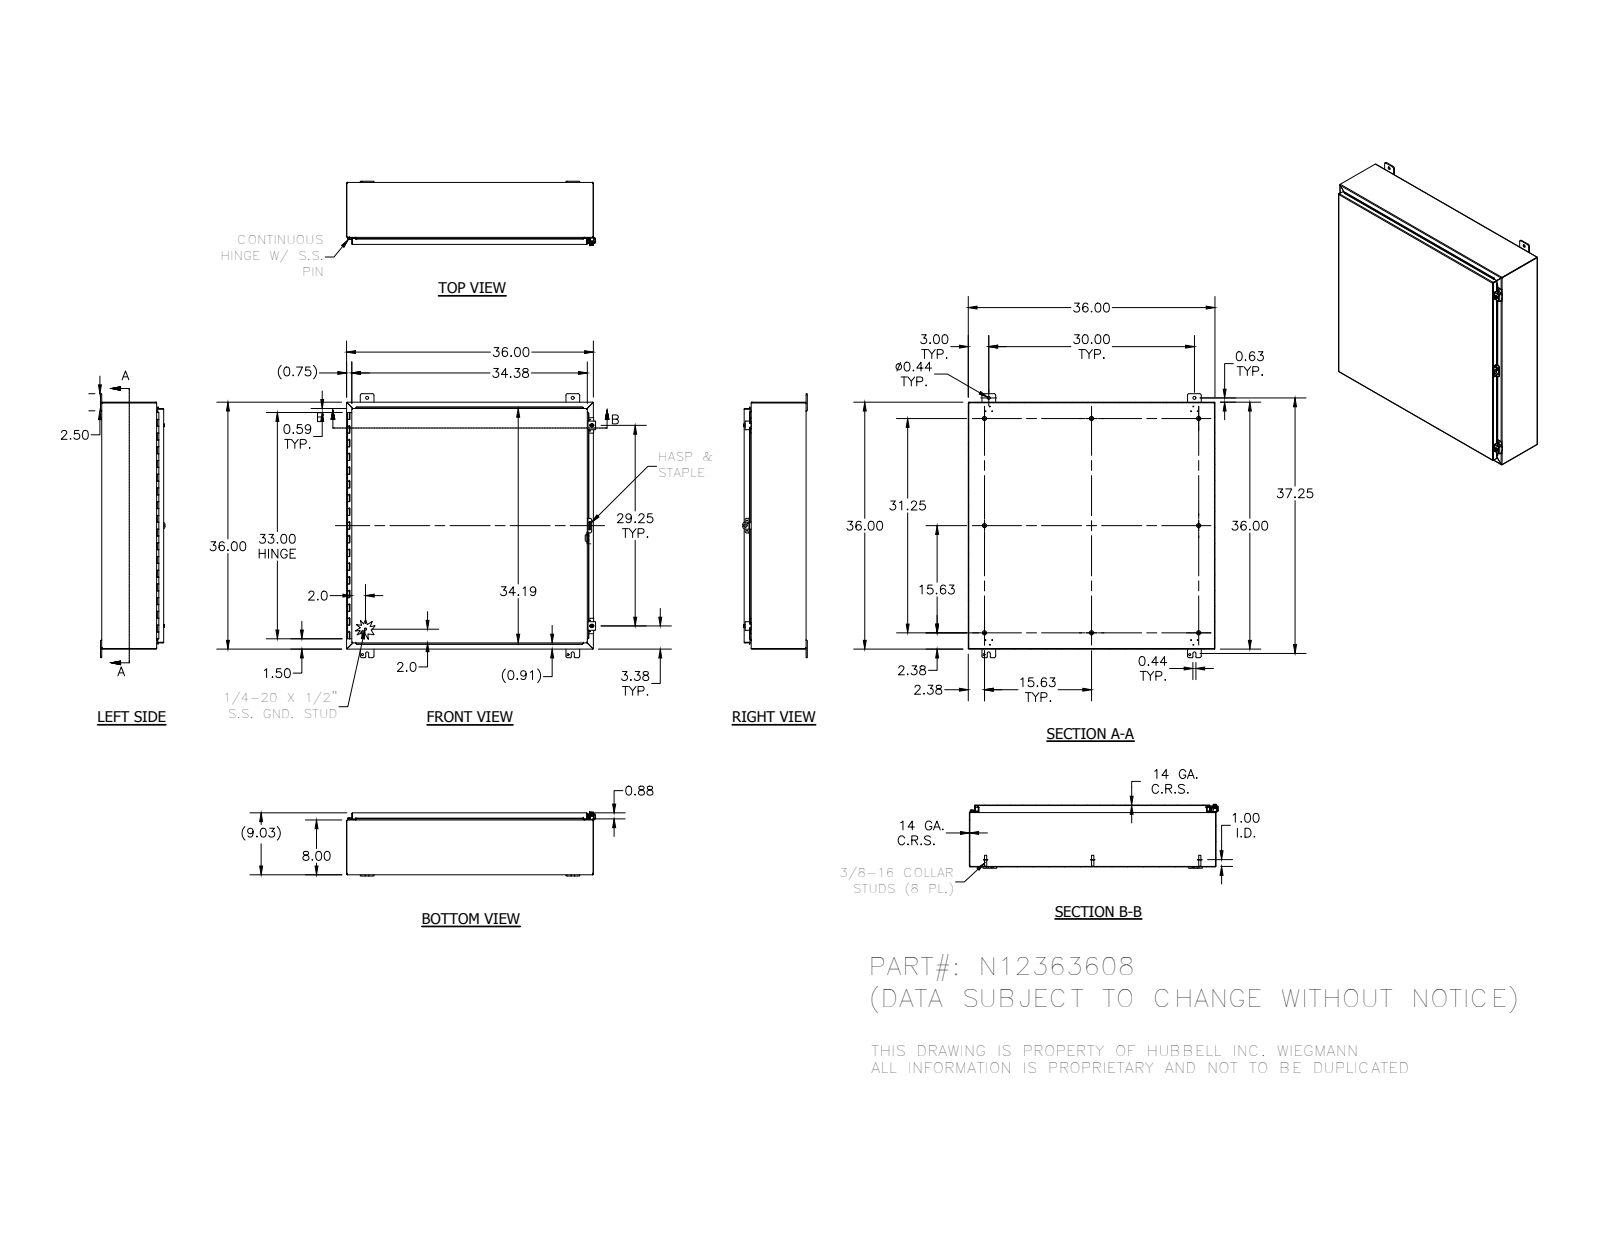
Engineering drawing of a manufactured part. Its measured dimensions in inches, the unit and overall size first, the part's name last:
Units: inches
Overall size (bounding box): 38.5 × 36.311 × 9.41
Round holes (diameter × count): ⌀0.12 ×12, ⌀0.11 ×7, ⌀0.313 ×4, ⌀0.438 ×4, ⌀0.211 ×2, ⌀0.281 ×2, ⌀0.3 ×2, ⌀0.125 ×1, ⌀0.156 ×1, ⌀0.5 ×1
Round bosses / shafts (diameter × count): ⌀0.625 ×8, ⌀0.33 ×8, ⌀0.25 ×4, ⌀0.52 ×2, ⌀0.5 ×2, ⌀0.35 ×2, ⌀0.115 ×2, ⌀0.337 ×1
Partial cylindrical surfaces — rounded edges, fillets, slot ends (radius × count): R0.03 ×27, R0.063 ×25, R0.125 ×25, R0.25 ×25, R0.031 ×23, R0.105 ×23, R0.07 ×8, R0.1 ×4
Main face-to-face distances: 0.074, 8.959, 8.885, 9.033, 35.926, 36, 35.852, 7.926, 1.033, 8
Hole centre spacings: 30, 0.759, 0.876, 0.876, 0.94, 0.969, 1.995, 3.887
Volume: 323.8 in³ · Surface area: 8 526 in²
Bodies: 31 solids, 1116 faces (615 planar, 380 cylindrical, 121 other)
Part name (STEP PRODUCT): N12363608; 34840; 38420; N12363608BKP (+8 more)
STEP written by: Autodesk Inventor 2012 (AUTOMOTIVE_DESIGN)
